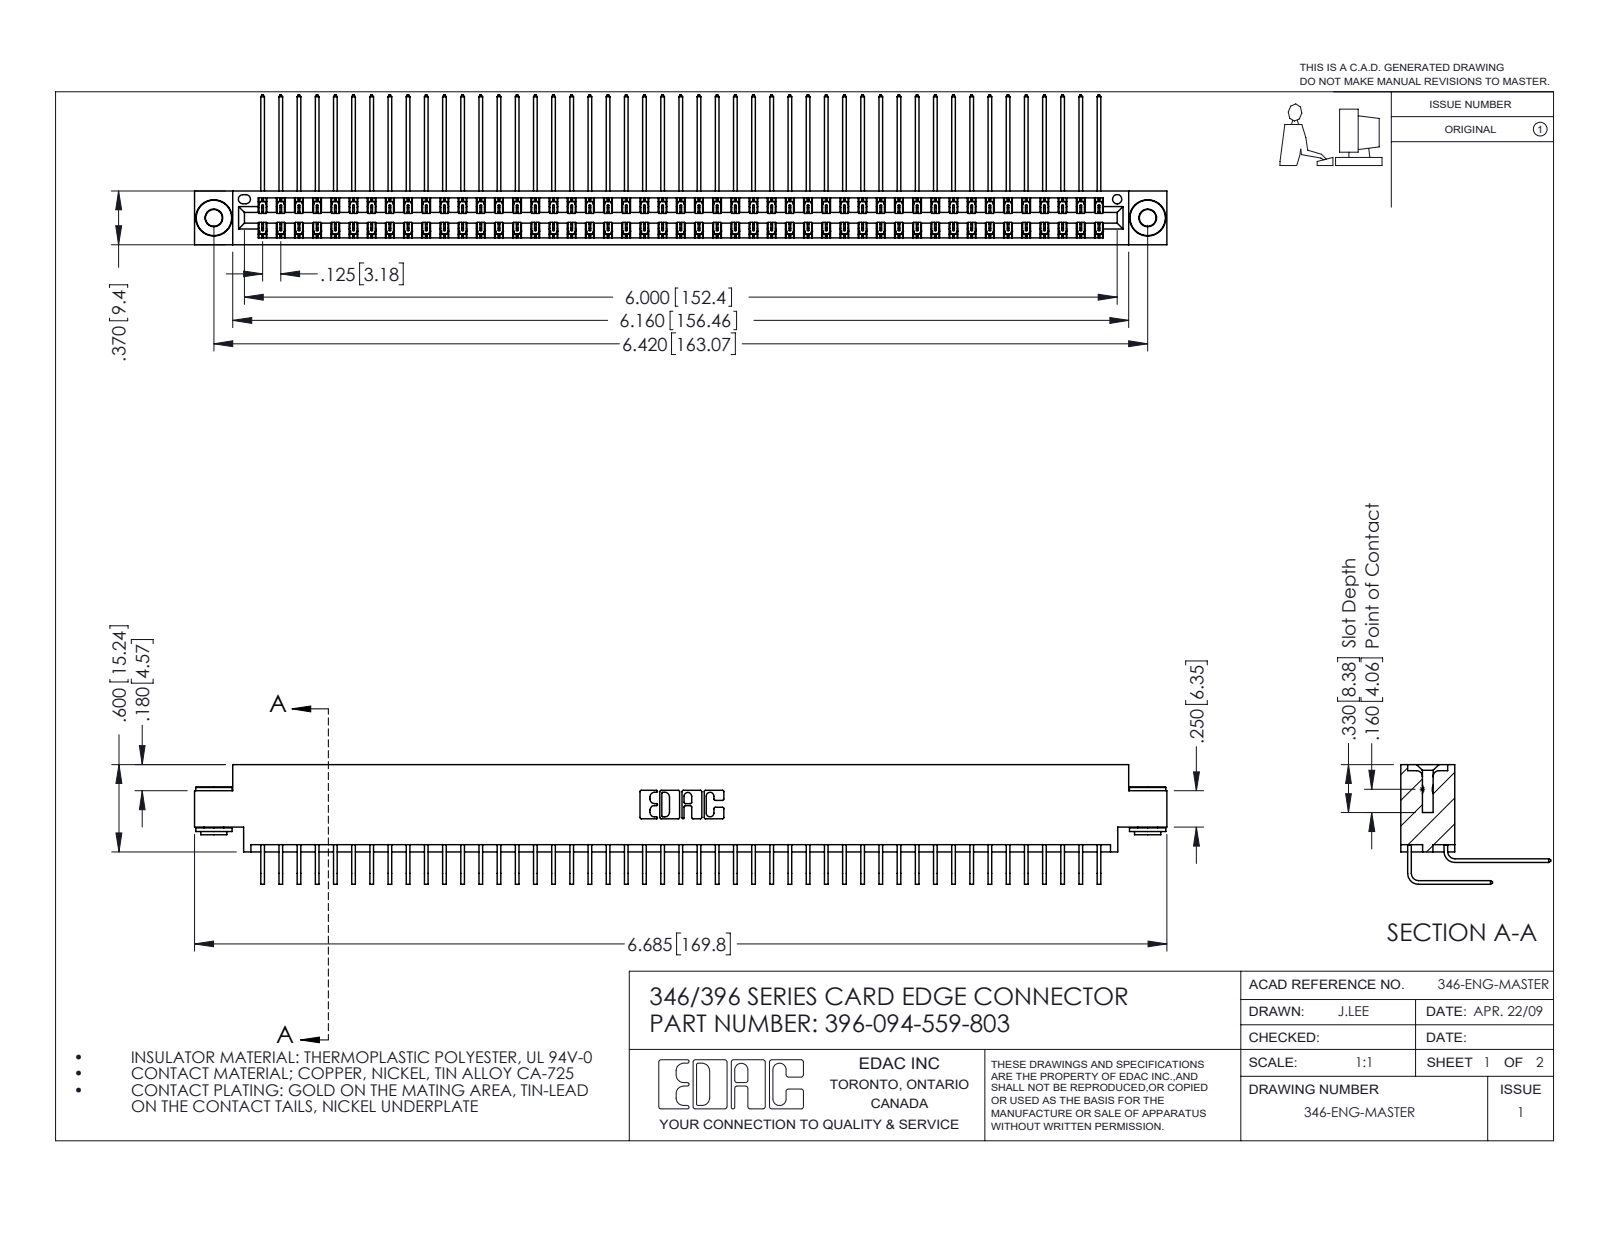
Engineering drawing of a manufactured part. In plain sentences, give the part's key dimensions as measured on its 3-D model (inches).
The part is named "345-292-001_559 Tail - 2; 345-292-001_558 559 Tail - 1; 345-250-002_345-250-002-102; 346 Part_0.170 Offset - 0.156 Dia-TH (+1 more)". Its 3-D file was written by "SolidWorks 2016 (CONFIG_CONTROL_DESIGN)". It is 97 solids with 5240 faces: 3568 planar, 1664 cylindrical and 8 other. Overall it measures 6.685 by 1.03 by 0.823 inches. Its volume is 1.038 cubic inches and its surface area 40.99 square inches. Round holes: 2 of diameter 0.116, 2 of diameter 0.156, 1 of diameter 0.064. Round bosses or shafts: 2 of diameter 0.25, 2 of diameter 0.18, 2 of diameter 0.136. Partial cylindrical surfaces (rounded edges, fillets, slot ends): 141 of radius 0.006, 22 of radius 0.01, 6 of radius 0.007, 6 of radius 0.031, 3 of radius 0.026, 2 of radius 0.014, 2 of radius 0.022, 2 of radius 0.024. The main face-to-face distances are 0.048, 0.322, 0.025, 0.37, 0.25, 0.072, 0.298, 0.275, 0.148, 0.222. The hole center spacings are 0.246, 6.211, 6.42.
